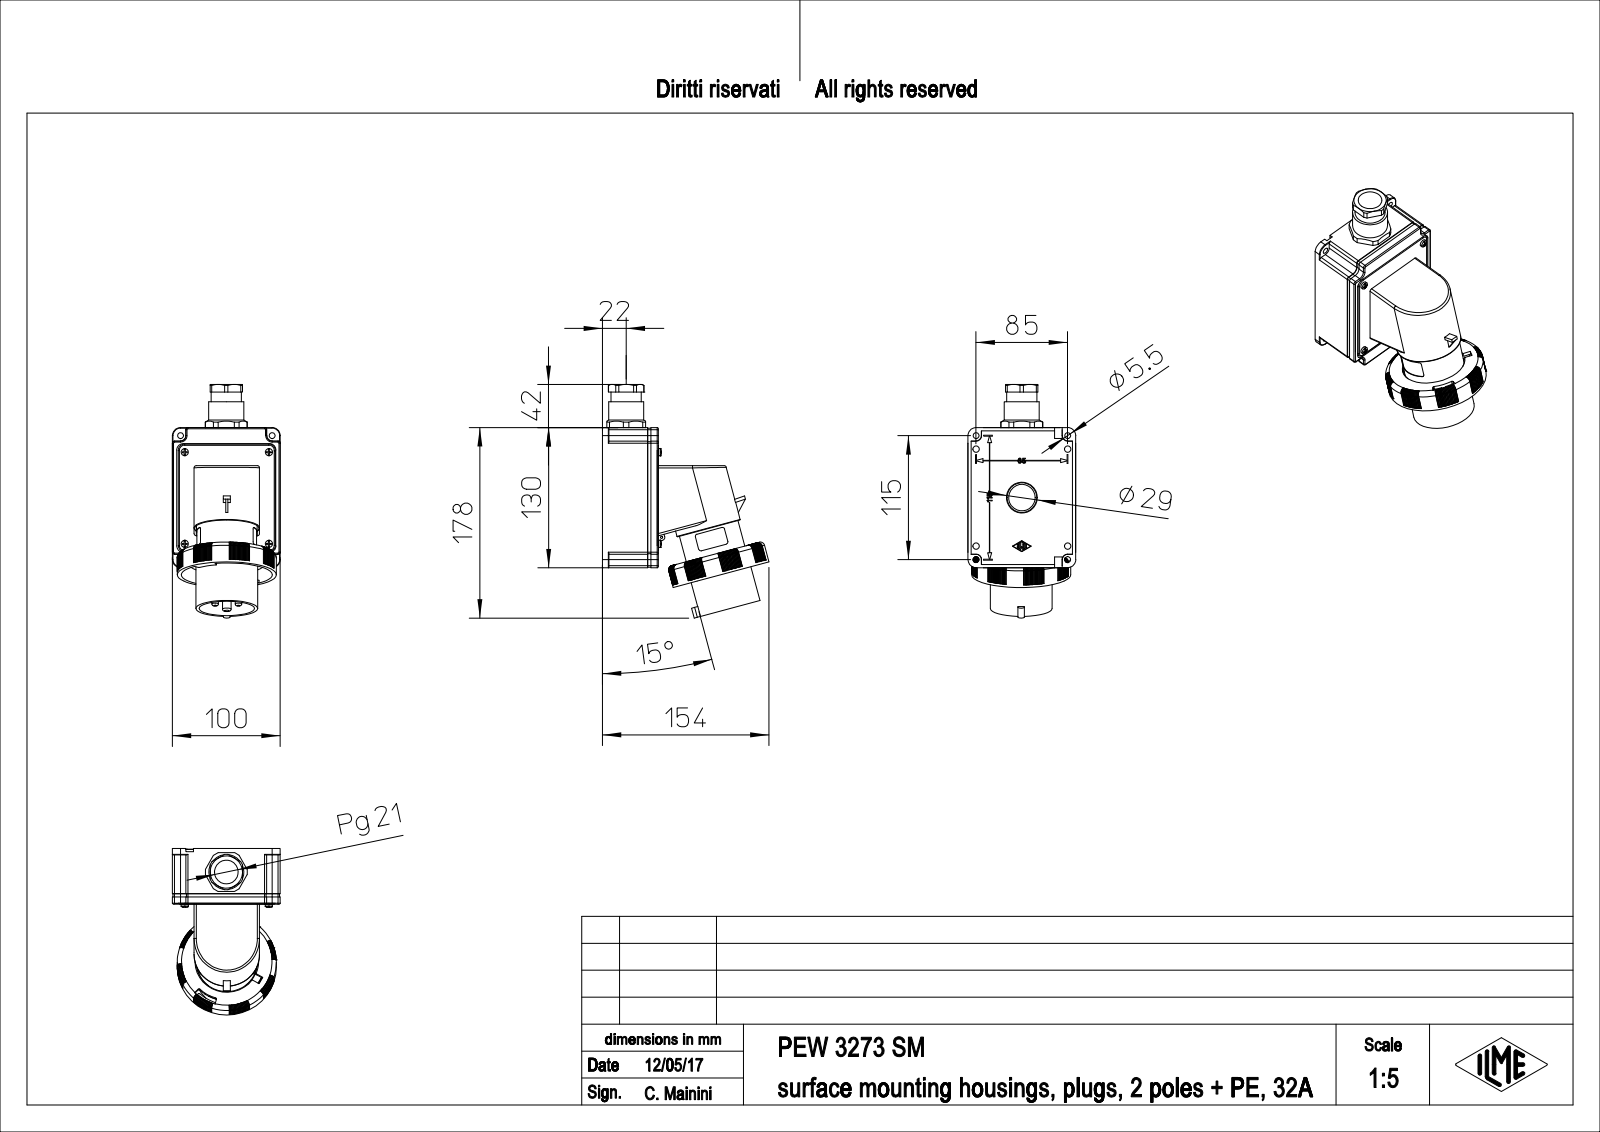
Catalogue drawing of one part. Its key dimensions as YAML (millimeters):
part_name: "PEW_3273_SM"
step_written_by: "PTC Creo Elements/Direct Modeling 19.0E 27-Jun-2016 (C) Parametric Technology GmbH (AUTOMOTIVE_DESIGN)"
units: millimeters
bodies: {solids: 1, faces: 1809, planar: 910, cylindrical: 379, other: 520}
overall_size: [216.68, 154.57, 100]
volume: 971882
surface_area: 156731
round_holes:
  - {diameter: 5.5, count: 8}
  - {diameter: 6, count: 4}
  - {diameter: 4, count: 2}
  - {diameter: 4.2, count: 2}
  - {diameter: 6.1, count: 2}
  - {diameter: 28.6, count: 2}
  - {diameter: 2, count: 1}
  - {diameter: 22, count: 1}
  - {diameter: 84.5, count: 1}
round_bosses_or_shafts:
  - {diameter: 6.7, count: 6}
  - {diameter: 6, count: 2}
  - {diameter: 3, count: 2}
  - {diameter: 92, count: 1}
  - {diameter: 70, count: 1}
  - {diameter: 60.7, count: 1}
  - {diameter: 57.3, count: 1}
  - {diameter: 56.2, count: 1}
partial_cylinders:
  - {radius: 3.6, count: 136}
  - {radius: 0.5, count: 18}
  - {radius: 1, count: 10}
  - {radius: 2, count: 10}
  - {radius: 41.53, count: 10}
  - {radius: 1.5, count: 8}
  - {radius: 6, count: 8}
  - {radius: 0.3, count: 4}
face_to_face_distances: [2, 4.5, 44.3, 50.8, 6.5, 46.3, 3, 100, 94.65, 6.85]
hole_center_spacings: [12.5, 85, 61.9, 71.5, 85.91, 102.5, 133.16, 21]
